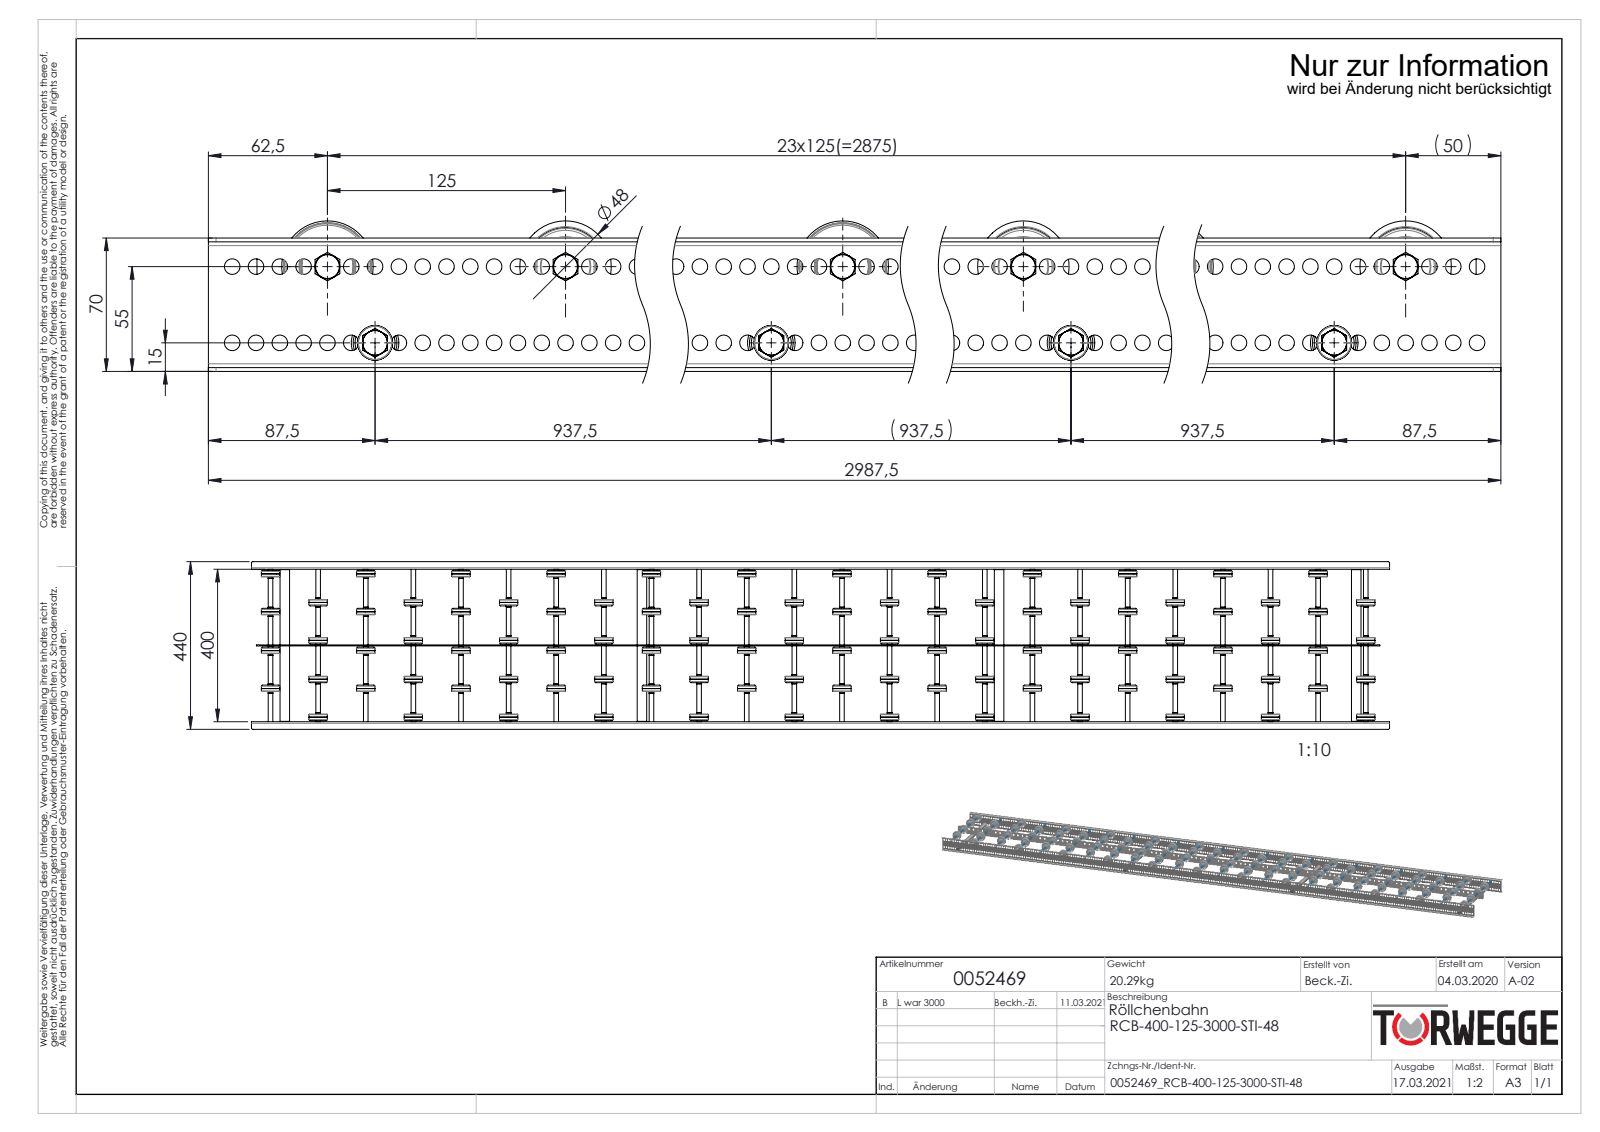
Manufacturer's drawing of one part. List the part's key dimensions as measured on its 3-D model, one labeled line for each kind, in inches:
Part name (STEP PRODUCT): Hutmutter_DIN_1587_M8; Traversen_KFG_L400; Profil_LRB-20x70x20x2_KFG_S109080_U-PROFIL-20-70-20-2-LRB-L=2987,5; Röllchenachse-für-Konfiguration_EL400 Stahl (+6 more)
STEP written by: SolidWorks 2020 (AUTOMOTIVE_DESIGN)
Units: inches
Bodies: 383 solids, 12450 faces (2370 planar, 5360 cylindrical, 4720 other)
Overall size (bounding box): 117.618 × 17.323 × 3.11
Volume: 279.2 in³ · Surface area: 5 733 in²
Round holes (diameter × count): ⌀0.323 ×476, ⌀0.335 ×118, ⌀0.262 ×24, ⌀0.315 ×24, ⌀0.38 ×24, ⌀0.591 ×24, ⌀1.614 ×24, ⌀0.268 ×4, ⌀0.827 ×4
Round bosses / shafts (diameter × count): ⌀1.89 ×24, ⌀0.512 ×24, ⌀0.492 ×24, ⌀0.488 ×24, ⌀0.472 ×24, ⌀0.453 ×24, ⌀0.984 ×4, ⌀0.315 ×4
Partial cylindrical surfaces — rounded edges, fillets, slot ends (radius × count): R0.157 ×8, R0.079 ×4, R0.197 ×4
Main face-to-face distances: 0.079, 15.827, 7.933, 7.913, 2.677, 3.917, 2.953, 15.906, 15.748, 0.472
Hole centre spacings: 0.492, 0.984, 1.476, 1.969, 2.461, 2.953, 3.445, 3.937
